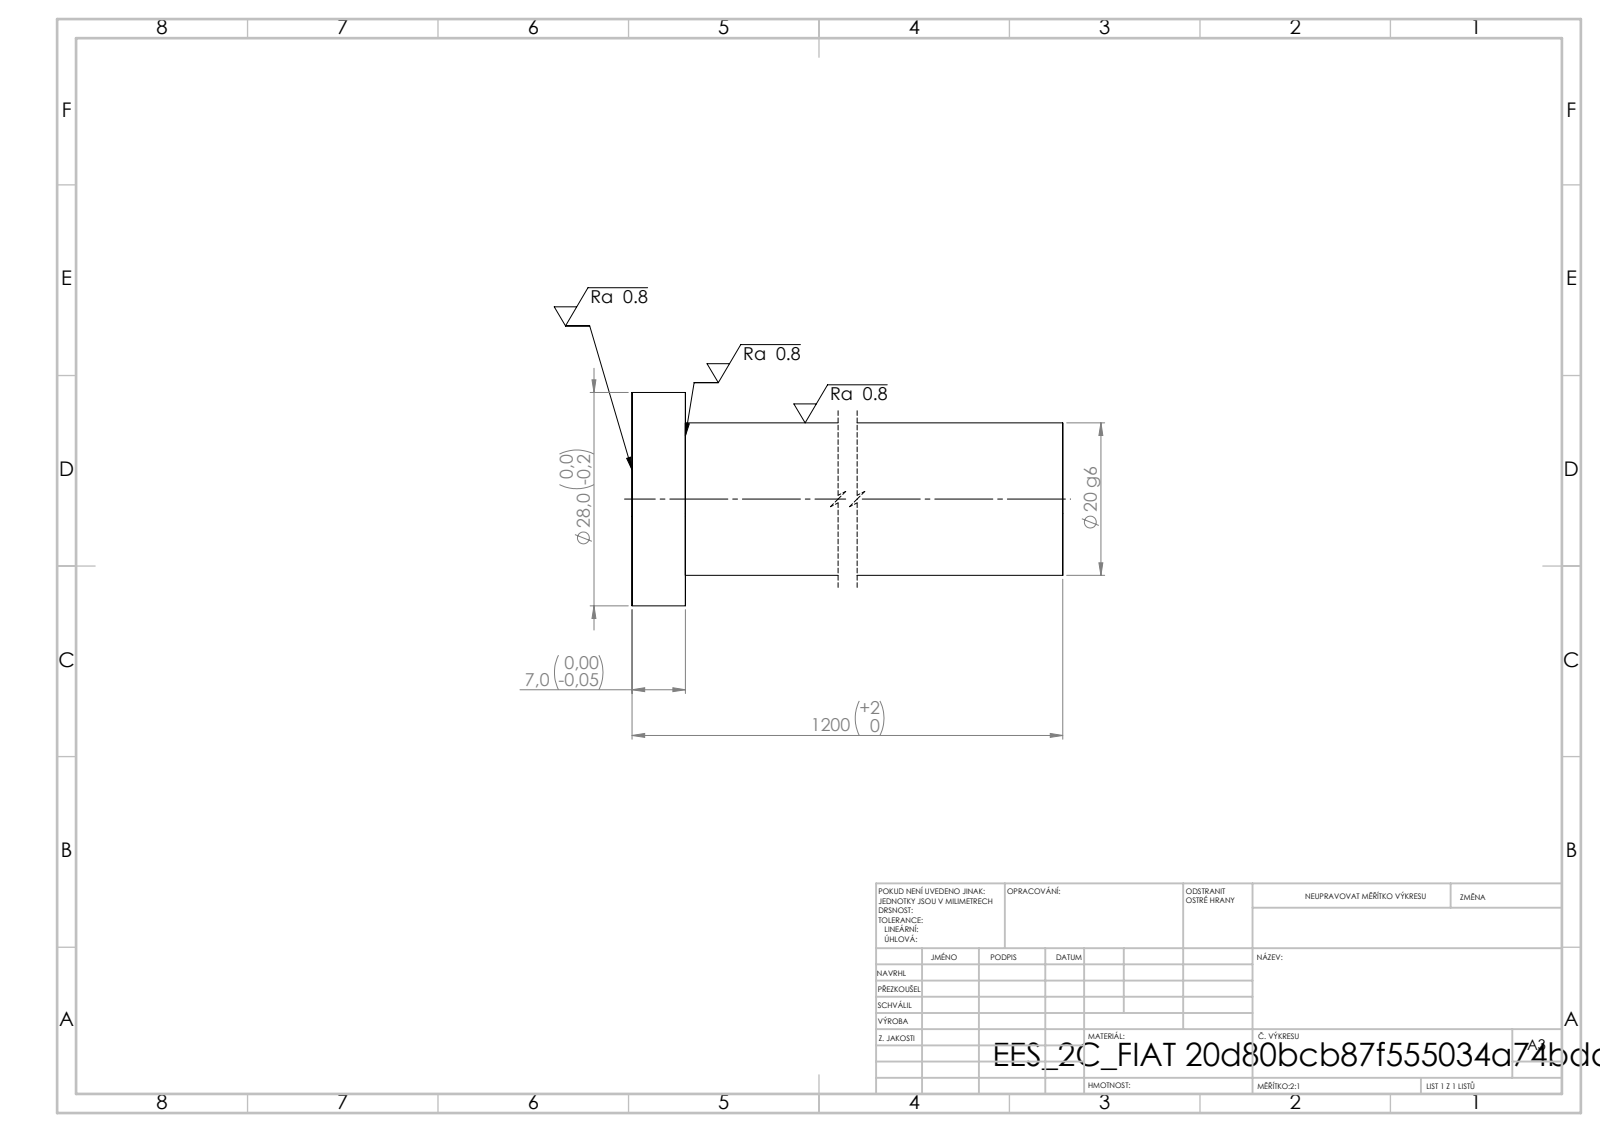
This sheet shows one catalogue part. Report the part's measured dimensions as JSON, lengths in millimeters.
{"step_written_by": "SolidWorks 2019 (CONFIG_CONTROL_DESIGN)", "units": "millimeters", "bodies": {"solids": 1, "faces": 7, "planar": 3, "cylindrical": 4, "other": 0}, "overall_size": [1200, 28, 28], "volume_mm3": 379102, "surface_area_mm2": 76806, "round_bosses_or_shafts": [[28, 1], [20, 1]], "face_to_face_distances": [1200, 7, 1193]}
